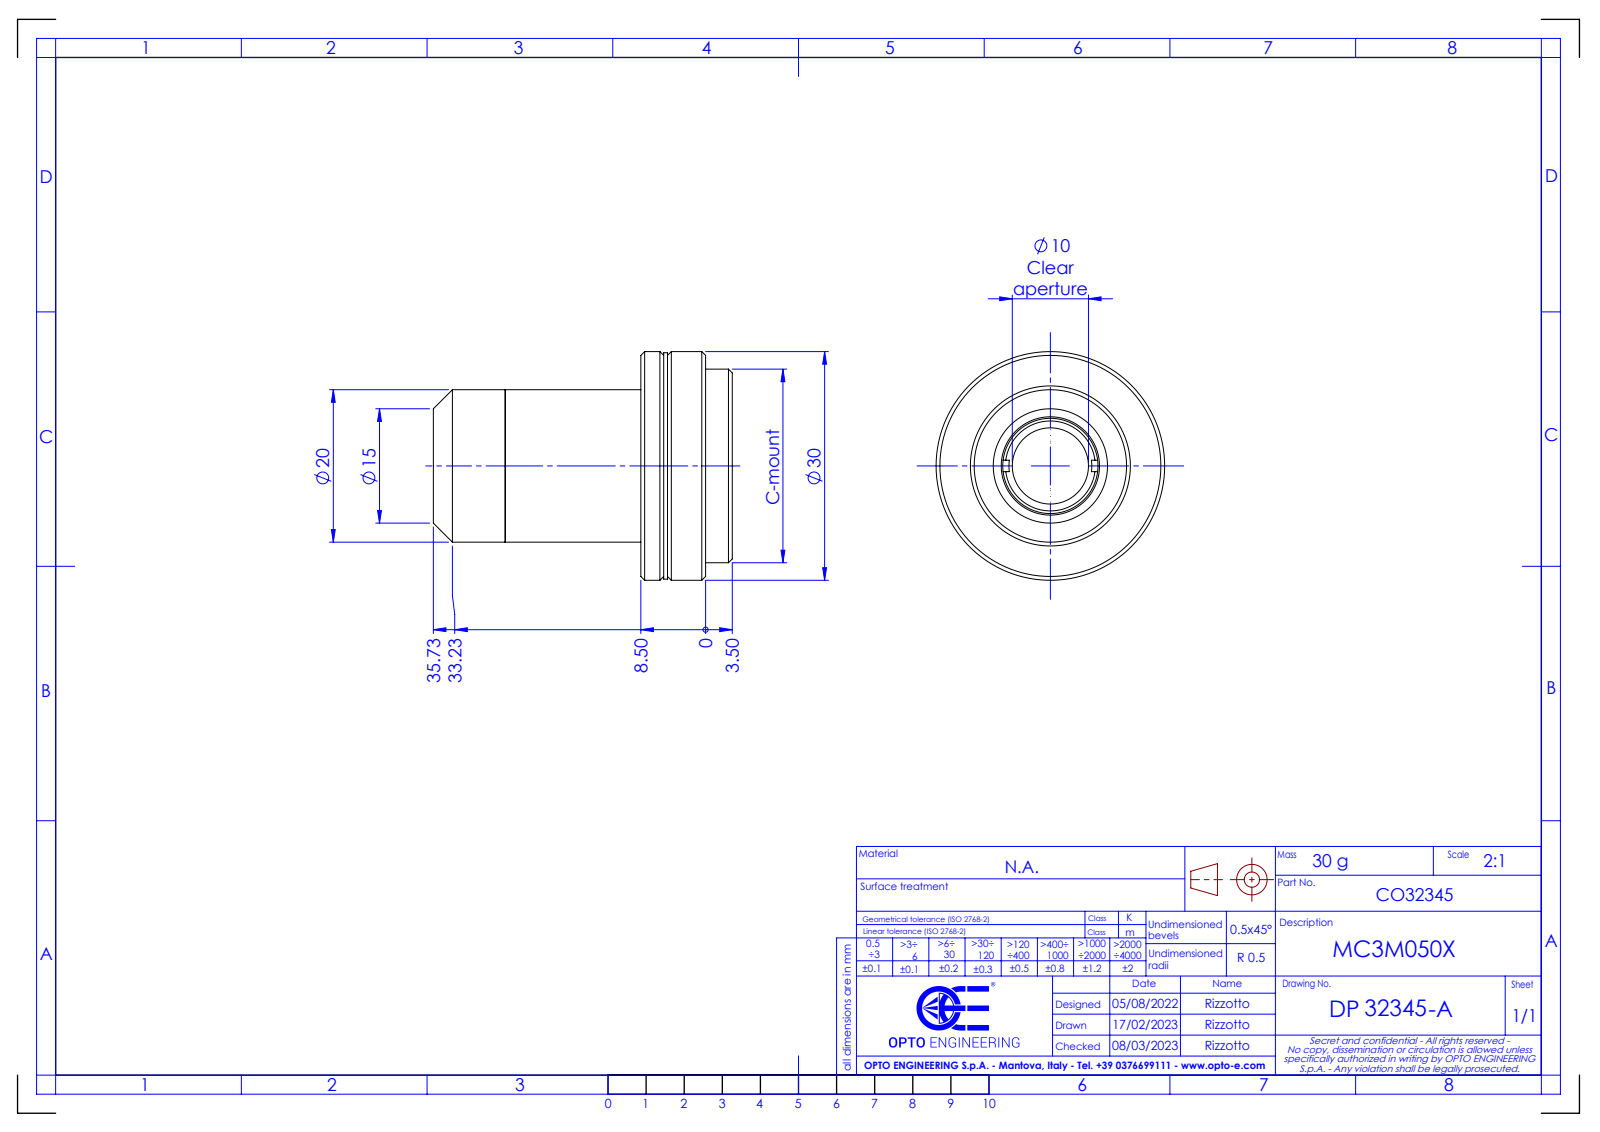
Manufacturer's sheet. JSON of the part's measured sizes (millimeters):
{"part_name": "DP32345-A_MC3M050X", "step_written_by": "SolidWorks 2021 (CONFIG_CONTROL_DESIGN)", "units": "millimeters", "bodies": {"solids": 0, "faces": 69, "planar": 19, "cylindrical": 22, "other": 28}, "overall_size": [39.23, 30, 30], "round_holes": [[10, 1], [12.5, 1], [15.5, 1], [18, 1]], "round_bosses_or_shafts": [[30, 1], [29.7, 1], [25.4, 1], [20, 1]], "face_to_face_distances": [8.5, 3.5, 5, 3, 0.5, 5.5, 12, 9, 17.81, 20.81]}
